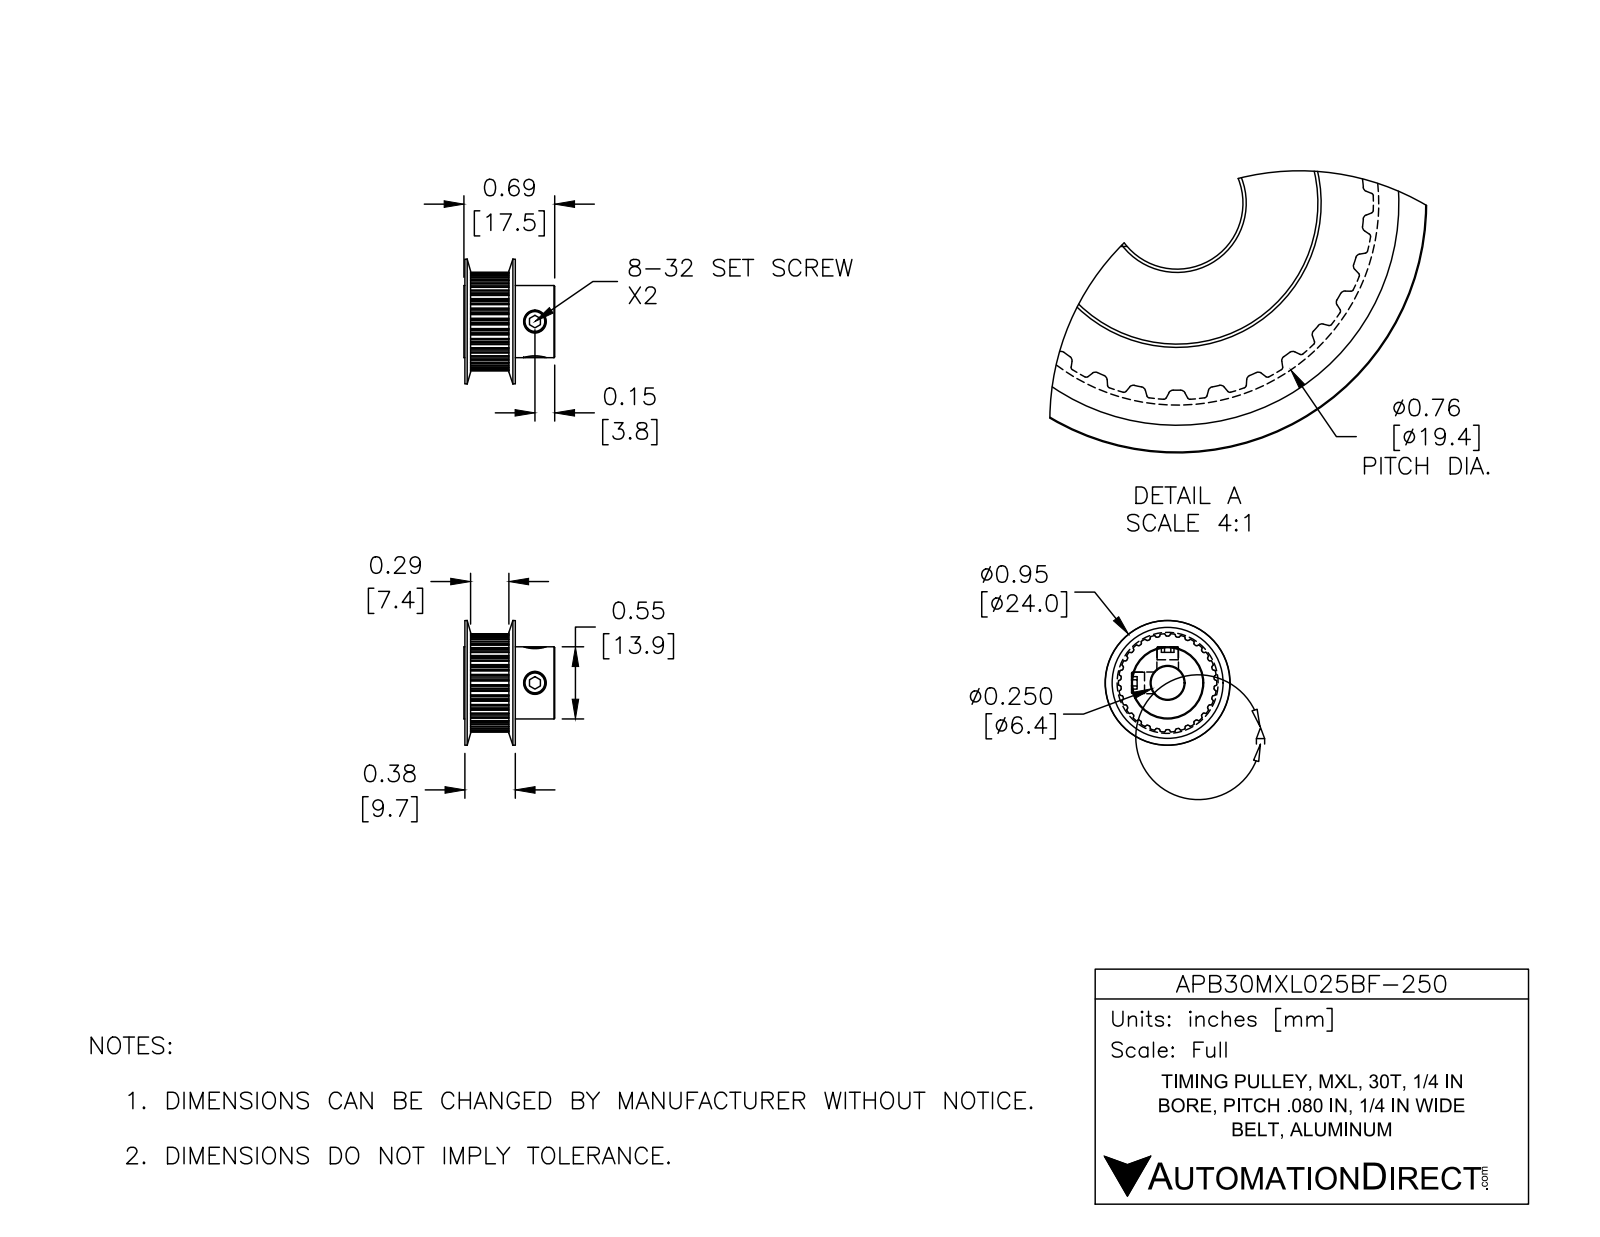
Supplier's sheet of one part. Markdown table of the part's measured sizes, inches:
| quantity | value |
| --- | --- |
| part name | APB30MXL025BF-250 |
| STEP written by | SolidWorks 2016 (AUTOMOTIVE_DESIGN) |
| units | inches |
| bodies | 3 solids, 325 faces (84 planar, 215 cylindrical, 26 other) |
| overall size | 0.945 × 0.945 × 0.688 |
| volume | 0.199 in³ |
| surface area | 4.225 in² |
| round holes (diameter × count) | 0.164 × 2, 0.25 × 1 |
| round bosses / shafts (diameter × count) | 0.16 × 2, 0.546 × 1 |
| partial cylindrical surfaces (radius × count) | 0.005 × 60, 0.009 × 60, 0.354 × 1, 0.372 × 1 |
| main face-to-face distances | 0.346, 0.025, 0.37, 0.687, 0.663, 0.317, 0.31, 0.05, 0.025, 0.32 |
